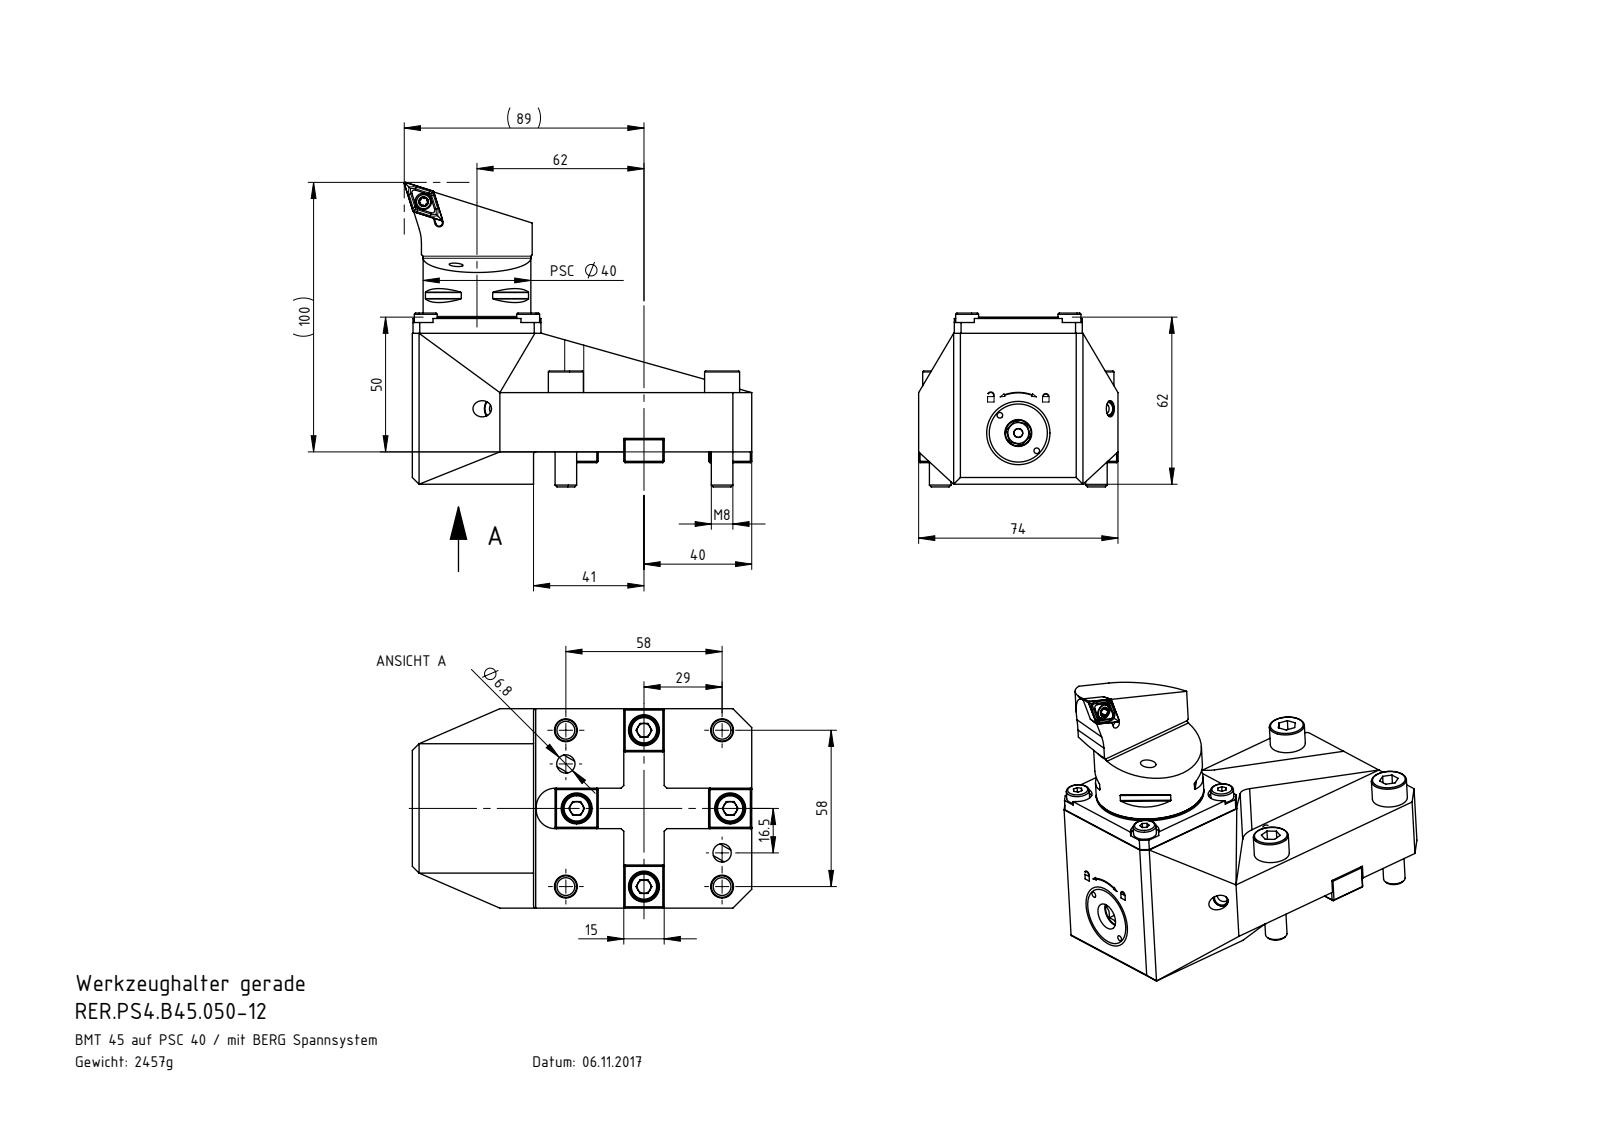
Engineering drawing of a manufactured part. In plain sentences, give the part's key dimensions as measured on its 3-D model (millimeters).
The part is named "DCMT11T304; RER.PS4.B45.050-12; KVT_MB_600_050; WCB-ER2.001.009_A (+8 more)". Its 3-D file was written by "SolidWorks 2017 (AUTOMOTIVE_DESIGN)". It is 56 solids with 1819 faces: 624 planar, 436 cylindrical and 759 other. Overall it measures 129.01 by 112.01 by 75 millimeters. Its volume is 337 361 cubic millimeters and its surface area 111 404 square millimeters. Round holes: 9 of diameter 5, 7 of diameter 4.2, 5 of diameter 2.5, 5 of diameter 6.5, 4 of diameter 3.3, 4 of diameter 5.5, 4 of diameter 7, 4 of diameter 8.4, 4 of diameter 8.5, 4 of diameter 11, 2 of diameter 2, 2 of diameter 4. Round bosses or shafts: 6 of diameter 16, 6 of diameter 6, 6 of diameter 5, 4 of diameter 10, 4 of diameter 8.5, 4 of diameter 8, 2 of diameter 5.5, 2 of diameter 3. Partial cylindrical surfaces (rounded edges, fillets, slot ends): 8 of radius 0.3, 8 of radius 4, 6 of radius 0.34, 6 of radius 0.59, 4 of radius 5.25, 3 of radius 3, 2 of radius 0.8, 2 of radius 7. The main face-to-face distances are 22, 17, 15, 45, 5, 27.5, 54, 47.5, 75, 19.6. The hole center spacings are 58, 26.87, 29, 38, 64.85, 9.5, 12.5, 12.69.
